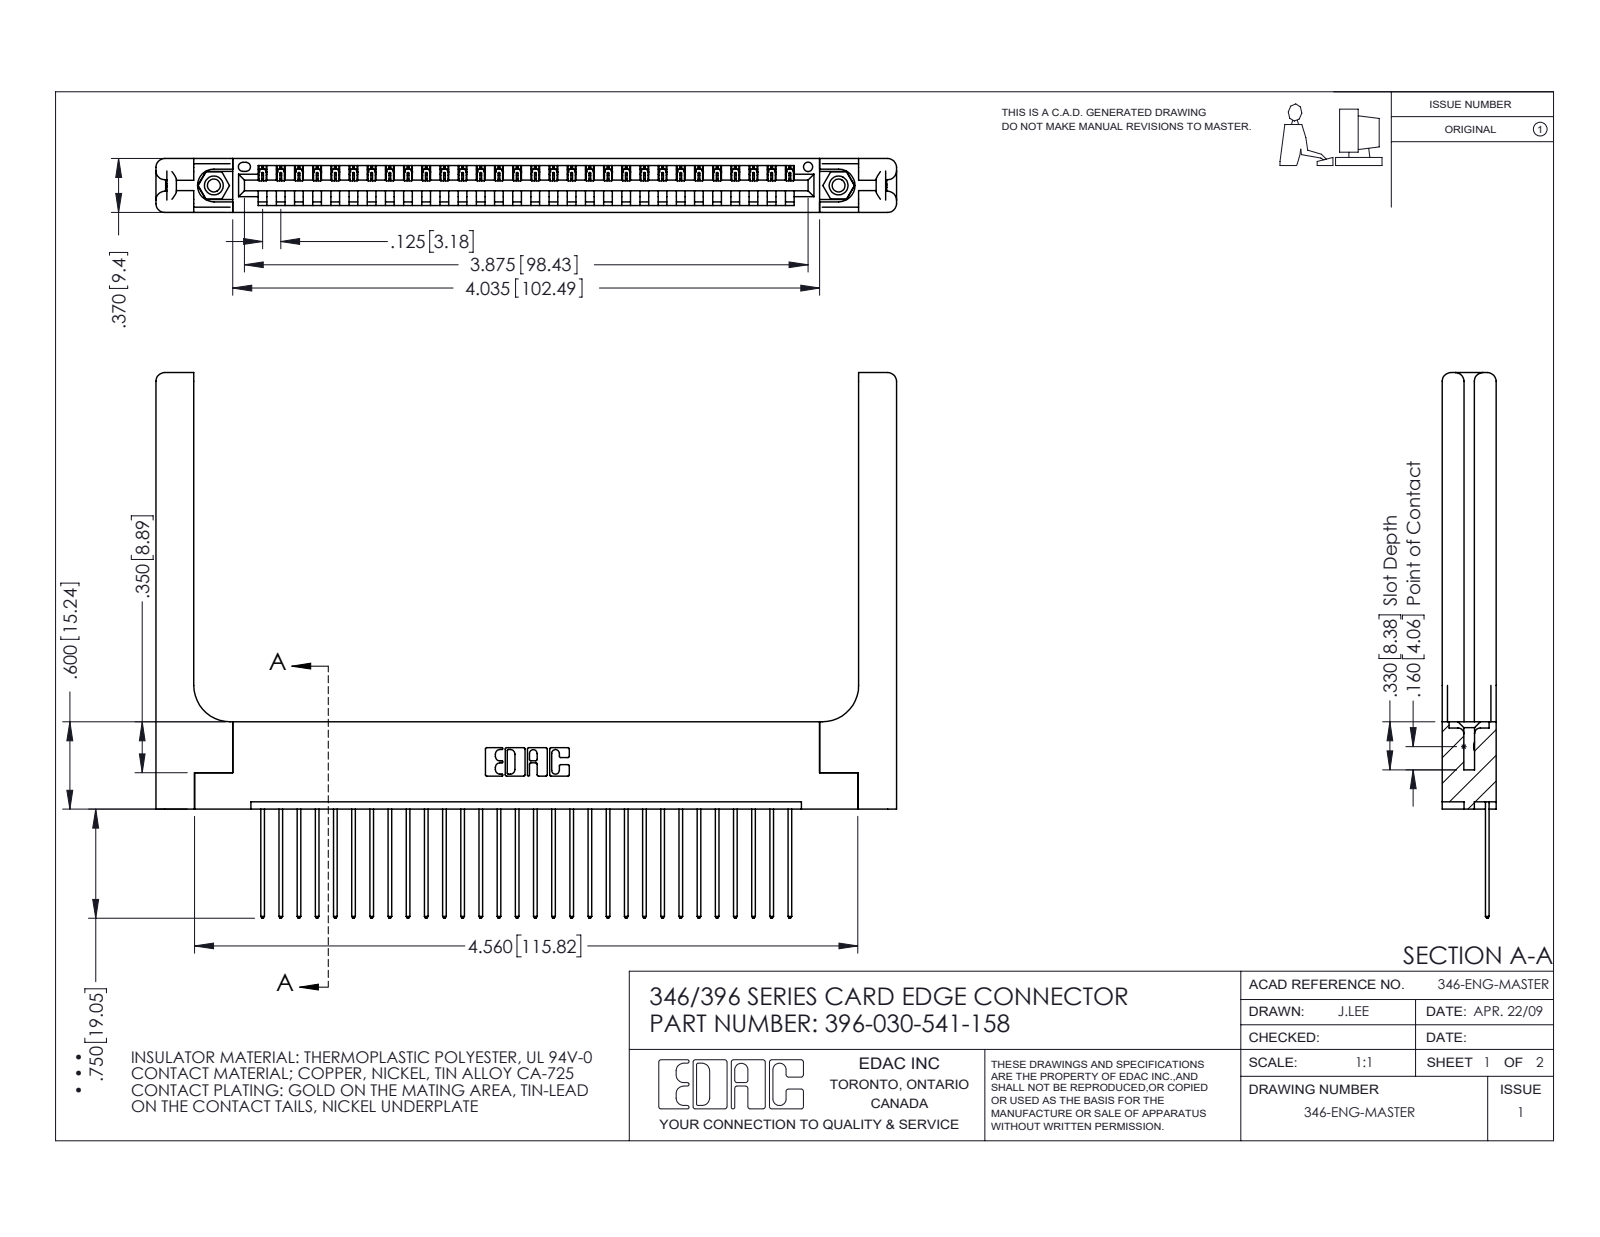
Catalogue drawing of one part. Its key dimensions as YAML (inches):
part_name: "345-292-001_345-293-141; 346 Part_Flush Mounting Lugs - 0.156 Dia-TH; 345-250-001_345-250-001-102; 346-220-058_345-220-058 (+1 more)"
step_written_by: "SolidWorks 2016 (CONFIG_CONTROL_DESIGN)"
units: inches
bodies: {solids: 35, faces: 2118, planar: 1424, cylindrical: 634, other: 60}
overall_size: [5.091, 3.75, 0.37]
volume: 1.215
surface_area: 32.74
round_holes:
  - {diameter: 0.089, count: 2}
  - {diameter: 0.125, count: 2}
  - {diameter: 0.156, count: 2}
  - {diameter: 0.064, count: 1}
round_bosses_or_shafts:
  - {diameter: 0.155, count: 2}
partial_cylinders:
  - {radius: 0.006, count: 60}
  - {radius: 0.01, count: 60}
  - {radius: 0.01, count: 22}
  - {radius: 0.06, count: 16}
  - {radius: 0.007, count: 6}
  - {radius: 0.031, count: 6}
  - {radius: 0.026, count: 3}
  - {radius: 0.03, count: 2}
face_to_face_distances: [0.37, 0.072, 0.048, 0.322, 0.148, 0.15, 0.25, 0.298, 0.025, 0.076]
hole_center_spacings: [0.246, 4.087, 4.295]
